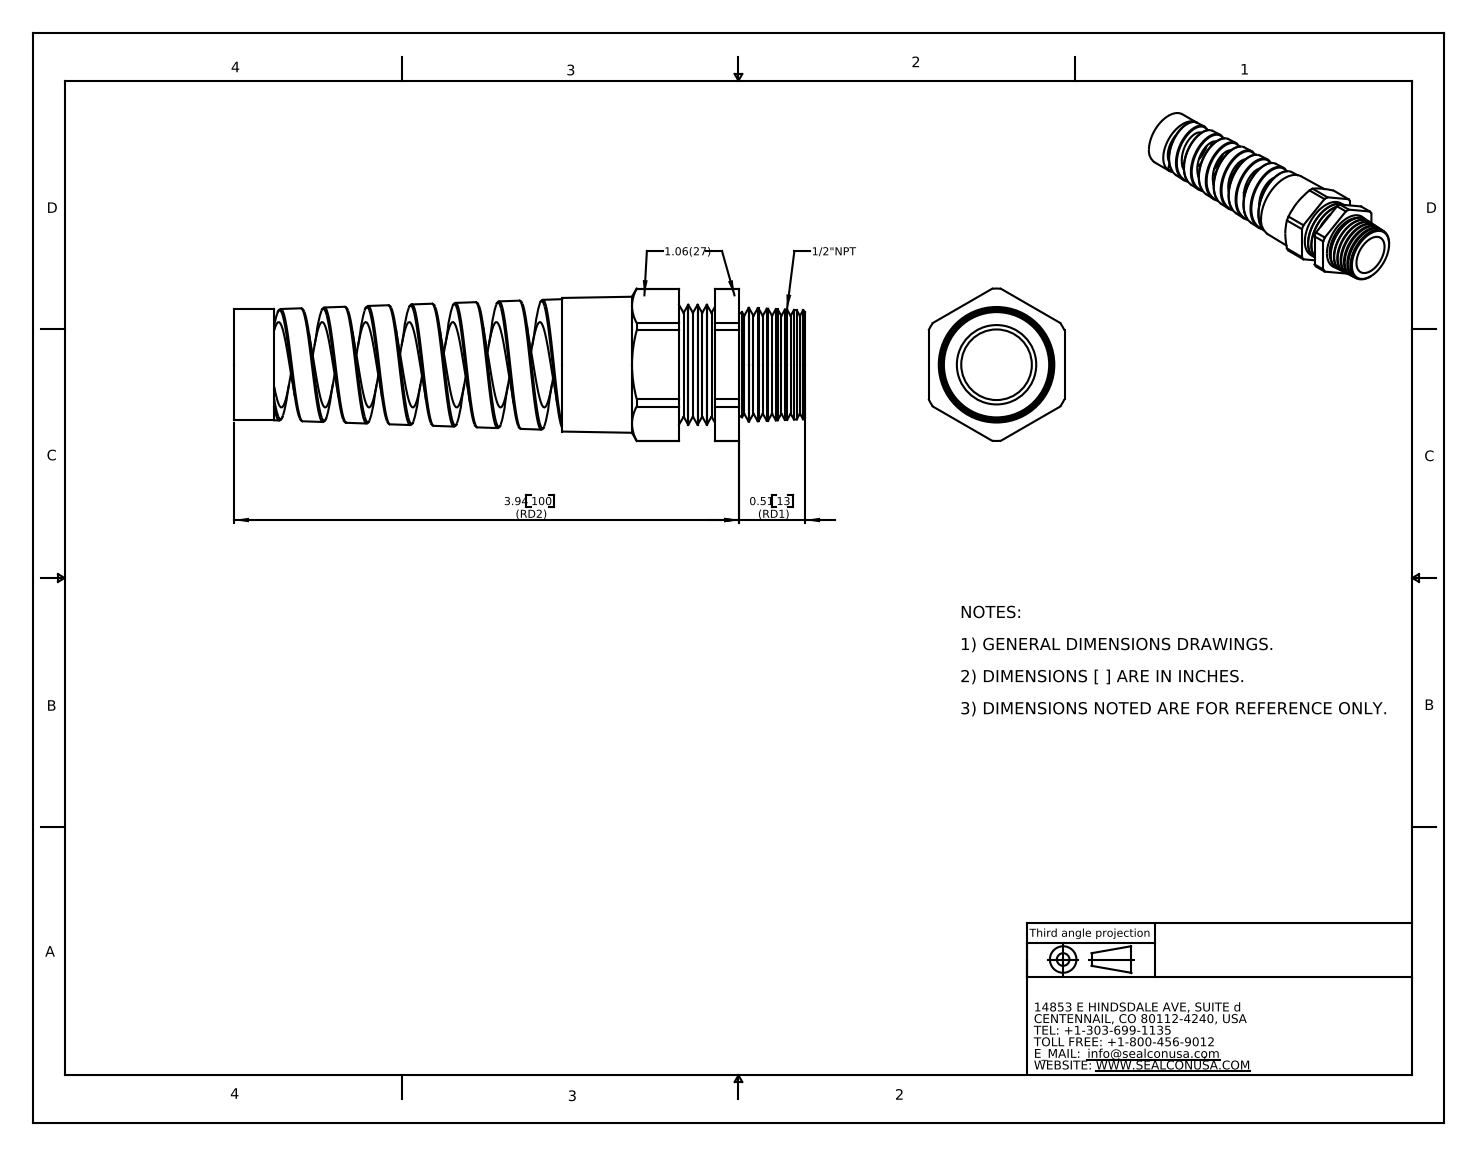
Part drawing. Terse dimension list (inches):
name: CF16NA-GY
written by: SolidWorks 2007 (CONFIG_CONTROL_DESIGN)
unit: in
bodies: 1 solid, 153 faces (19 planar, 39 cylindrical, 95 other)
size: 4.45 × 1.187 × 1.06
volume: 1.469 in³; area: 25.5 in²
holes: 1× ⌀0.55, 1× ⌀0.665
bosses: 1× ⌀0.933, 1× ⌀0.865
rounds: 1× R0.594
face distances: 1.06, 1.381, 0.91, 0.471, 1.187, 0.277, 0.194, 2.559, 3.469, 3.746
